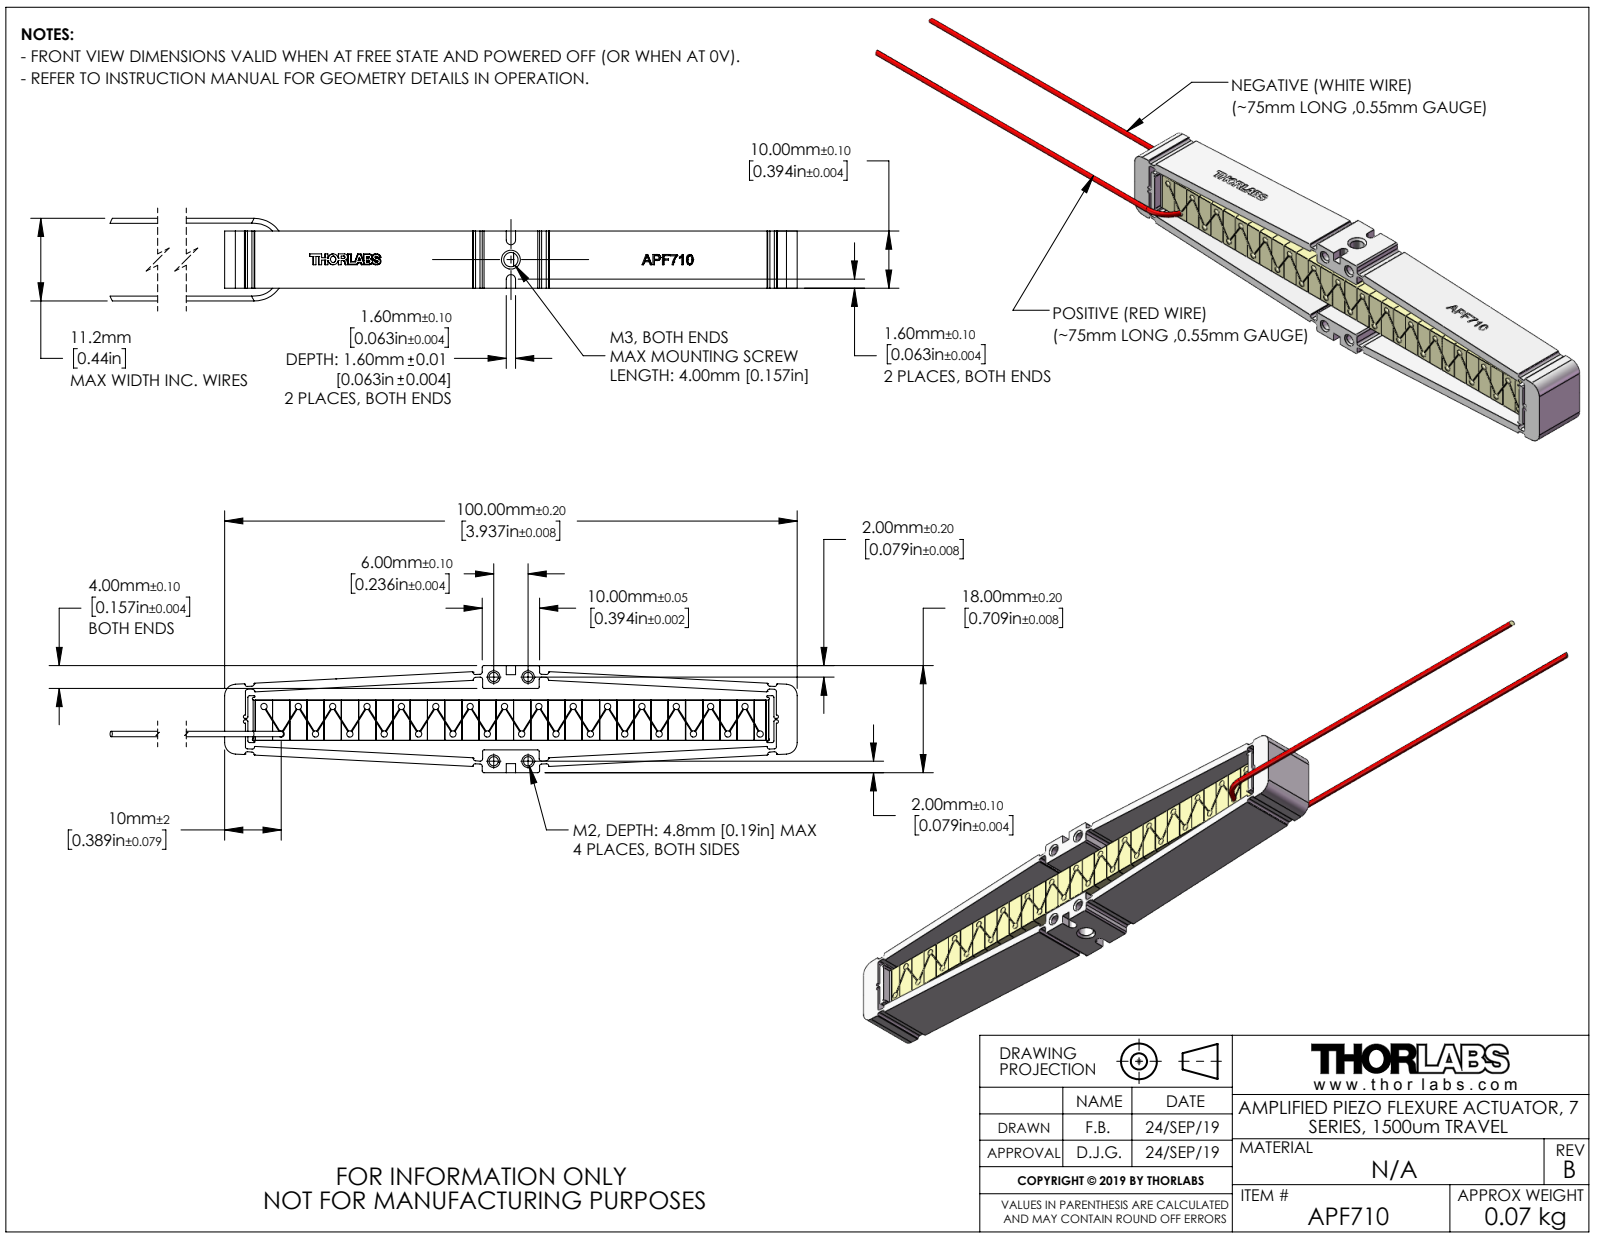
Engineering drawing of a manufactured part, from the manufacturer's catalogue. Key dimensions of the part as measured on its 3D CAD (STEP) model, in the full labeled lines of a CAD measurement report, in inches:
Part name (STEP PRODUCT): APF710
STEP written by: SolidWorks 2016 (CONFIG_CONTROL_DESIGN)
Units: inches
Bodies: 0 solids, 916 faces (397 planar, 243 cylindrical, 276 other)
Overall size (bounding box): 6.383 × 0.709 × 0.568
Round holes (diameter × count): ⌀0.063 ×4, ⌀0.074 ×1, ⌀0.098 ×1
Round bosses / shafts (diameter × count): ⌀0.043 ×28
Partial cylindrical surfaces — rounded edges, fillets, slot ends (radius × count): R0.016 ×32, R0.004 ×19, R0.012 ×19, R0.006 ×4, R0.009 ×4, R0.079 ×4, R0.031 ×2, R0.006 ×1
Main face-to-face distances: 0.276, 0.588, 0.06, 0.059, 0.335, 0.648, 0.528, 0.394, 0.035, 0.143
Hole centre spacings: 0.236, 0.551, 0.6
